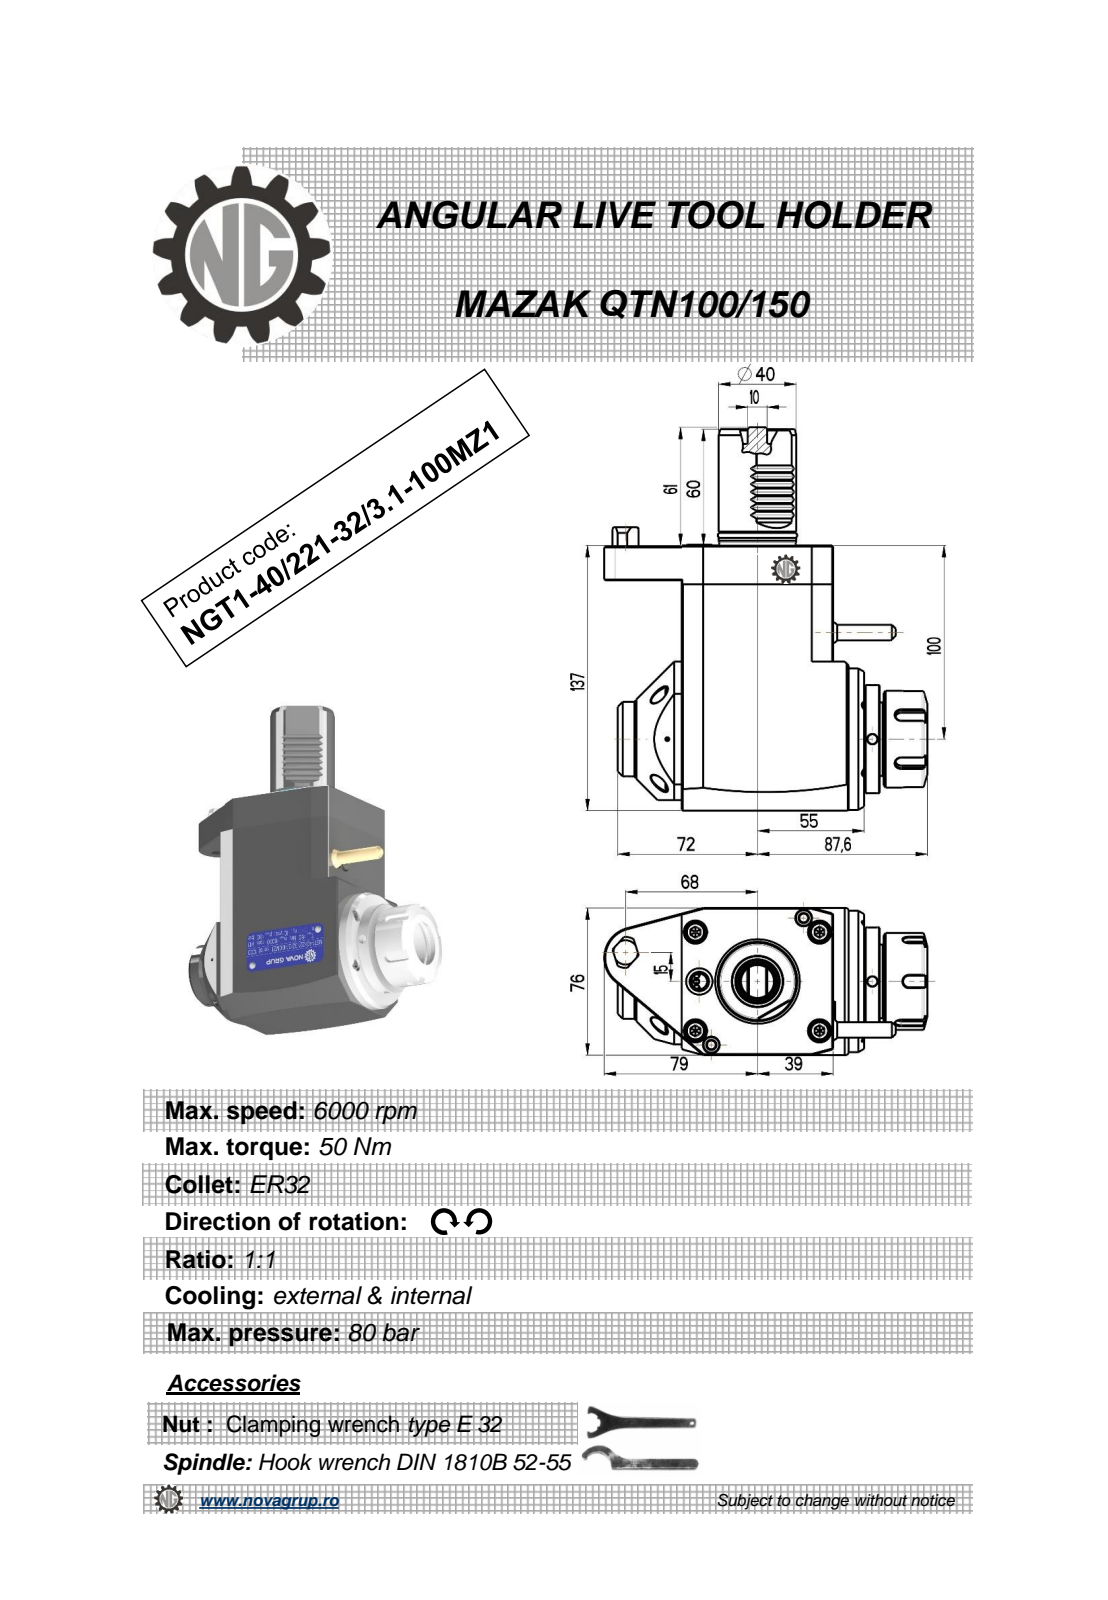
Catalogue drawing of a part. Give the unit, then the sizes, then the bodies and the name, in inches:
Units: inches
Overall size (bounding box): 7.795 × 6.559 × 2.992
Round holes (diameter × count): ⌀0.197 ×3, ⌀0.118 ×1, ⌀0.315 ×1, ⌀1.024 ×1, ⌀1.063 ×1
Round bosses / shafts (diameter × count): ⌀2.874 ×1, ⌀2.205 ×1, ⌀1.969 ×1, ⌀1.693 ×1, ⌀1.575 ×1, ⌀1.551 ×1, ⌀1.516 ×1, ⌀1.425 ×1
Partial cylindrical surfaces — rounded edges, fillets, slot ends (radius × count): R0.012 ×7, R0.008 ×6, R0.118 ×5, R0.031 ×2, R11.811 ×2, R0.315 ×1, R0.354 ×1, R0.624 ×1
Main face-to-face distances: 2.992, 3.071, 5.394, 0.315, 0.63, 4.685, 3.701, 0.709, 3.461, 0.295
Hole centre spacings: 1.181, 2.333, 2.379, 3.514
Volume: 68.22 in³ · Surface area: 129.6 in²
Bodies: 1 solid, 306 faces (133 planar, 78 cylindrical, 95 other)
Part name (STEP PRODUCT): NGT1_40_221_32_3_1_100MZ1
STEP written by: PRO/ENGINEER BY PARAMETRIC TECHNOLOGY CORPORATION, 2010280 (CONFIG_CONTROL_DESIGN)
